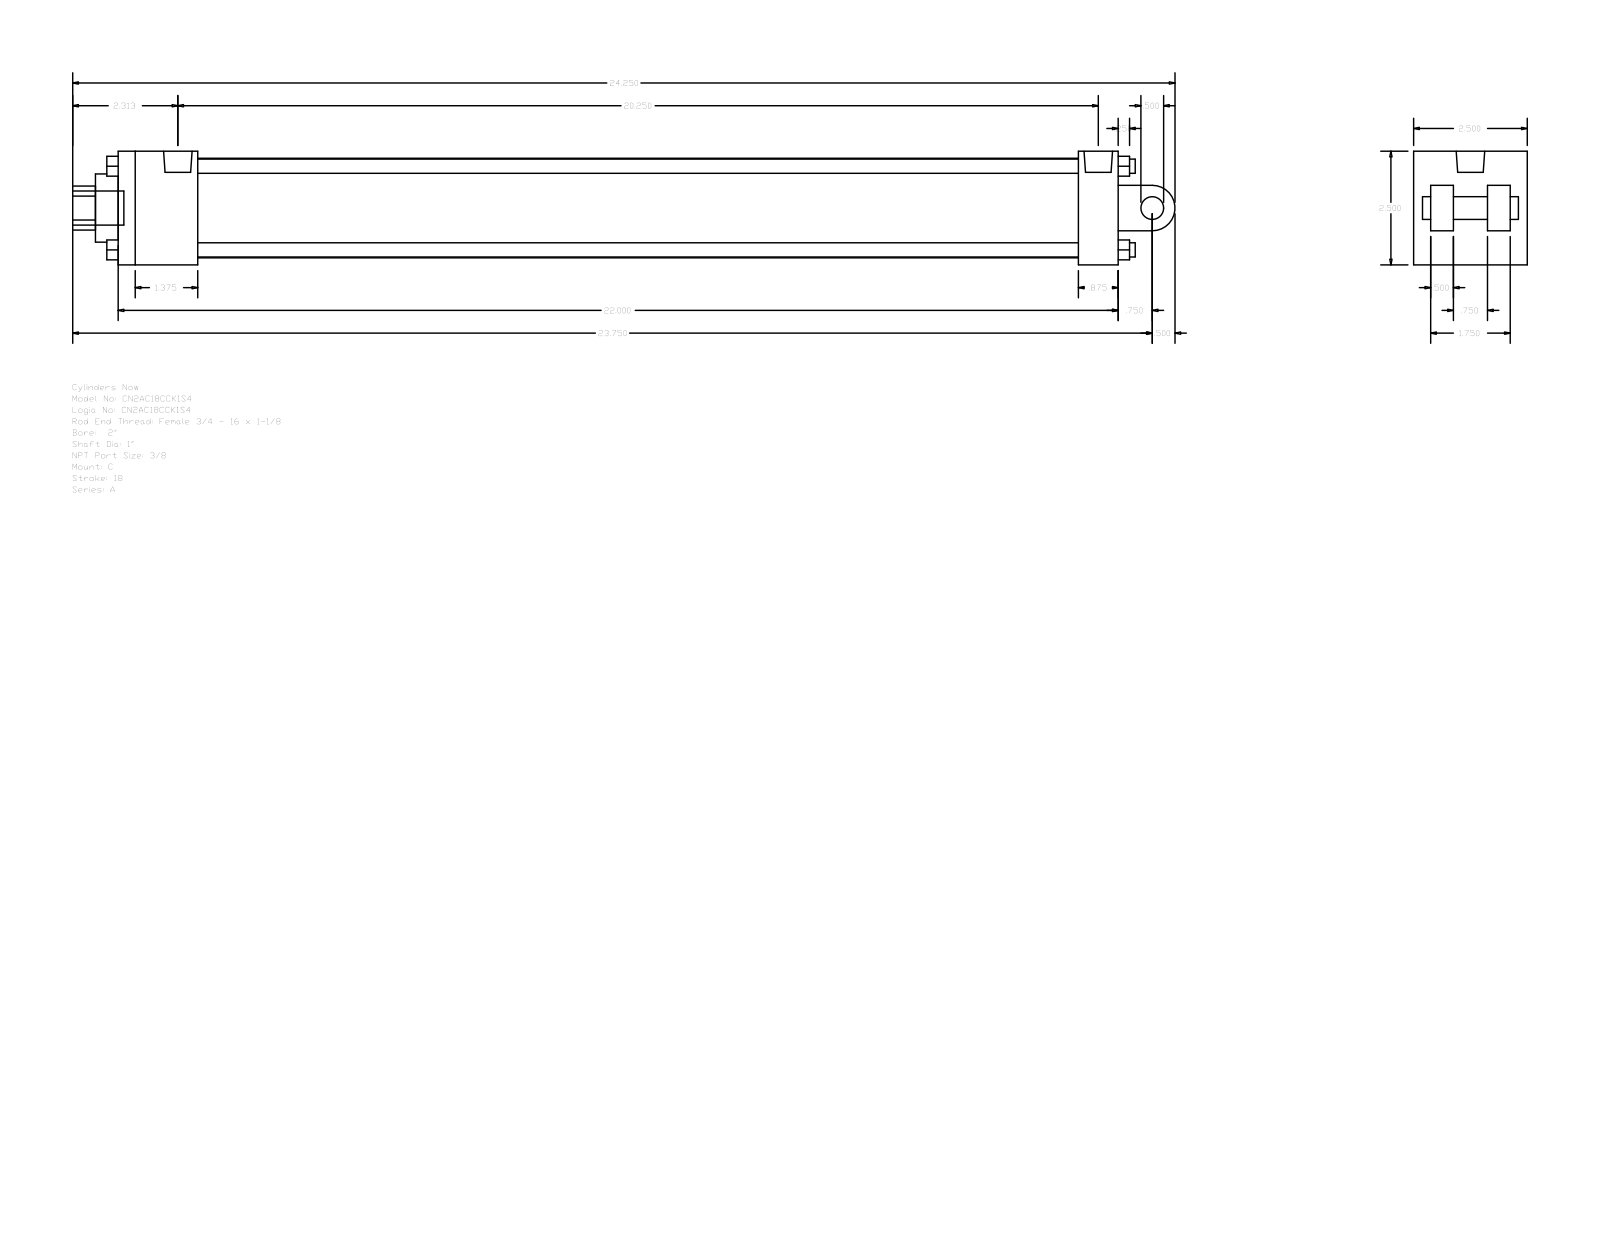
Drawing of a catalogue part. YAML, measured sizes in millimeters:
part_name: "A_C__0200_1"
step_written_by: "GSSL Pune (CONFIG_CONTROL_DESIGN)"
units: millimeters
bodies: {solids: 0, faces: 135, planar: 102, cylindrical: 33, other: 0}
overall_size: [615.95, 63.5, 63.5]
round_holes:
  - {diameter: 5.56, count: 2}
  - {diameter: 15.93, count: 1}
  - {diameter: 25.4, count: 1}
  - {diameter: 38.1, count: 1}
  - {diameter: 55.63, count: 1}
round_bosses_or_shafts:
  - {diameter: 7.94, count: 4}
  - {diameter: 5.56, count: 2}
  - {diameter: 19.05, count: 1}
  - {diameter: 15.93, count: 1}
  - {diameter: 12.7, count: 1}
partial_cylinders:
  - {radius: 12.29, count: 1}
  - {radius: 12.7, count: 1}
face_to_face_distances: [63.5, 22.22, 558.8, 44.45, 12.7, 9.52, 41.28, 514.35, 536.58, 492.13]
hole_center_spacings: [3.98]
